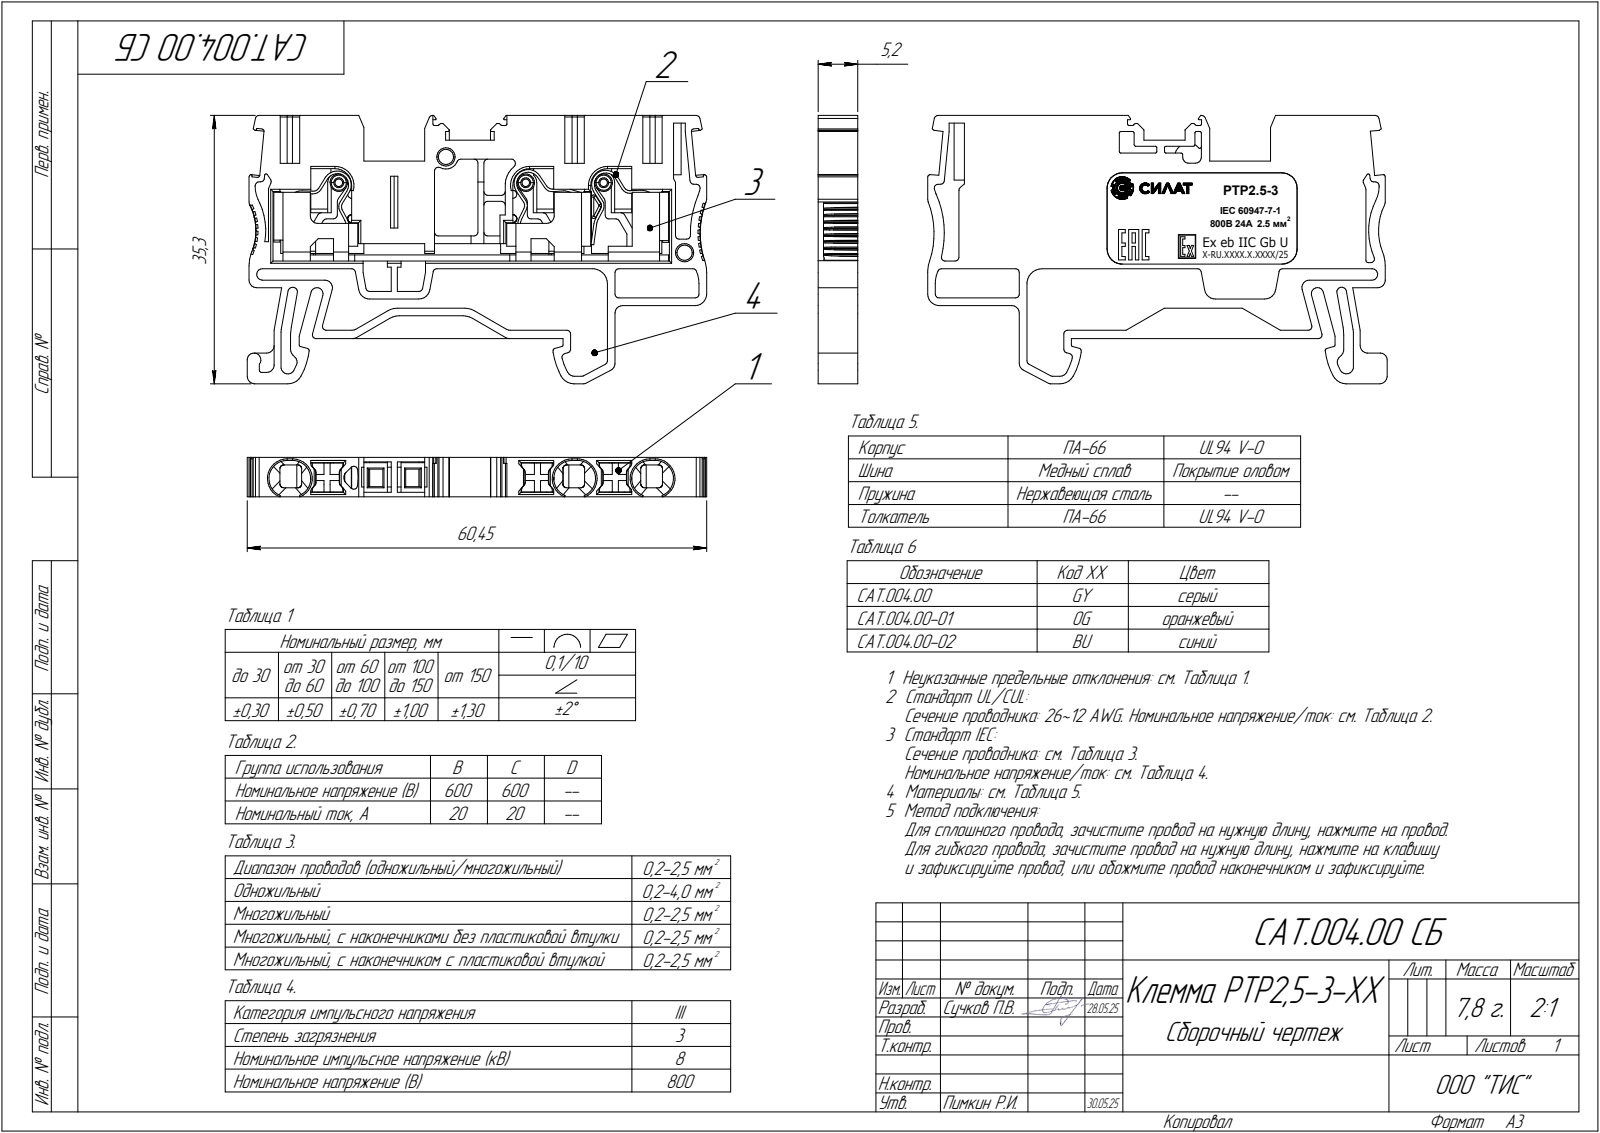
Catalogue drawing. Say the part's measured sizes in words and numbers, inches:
The part is named "Клемма PTP2,5-3-XX". Its 3-D file was written by "SolidWorks 2024 (AUTOMOTIVE_DESIGN)". It is 1 solid with 517 faces: 334 planar, 175 cylindrical and 8 other. Overall it measures 2.38 by 1.39 by 0.205 inches. Its volume is 0.48 cubic inches and its surface area 7.845 square inches. Partial cylindrical surfaces (rounded edges, fillets, slot ends): 57 of radius 0.02, 38 of radius 0.006, 9 of radius 0.012, 9 of radius 0.039, 7 of radius 0.008, 6 of radius 0.094, 3 of radius 0.079, 3 of radius 0.197. The main face-to-face distances are 0.205, 1.156, 0.165, 0.024, 0.973, 0.183, 0.035, 0.13, 0.909, 0.171.
